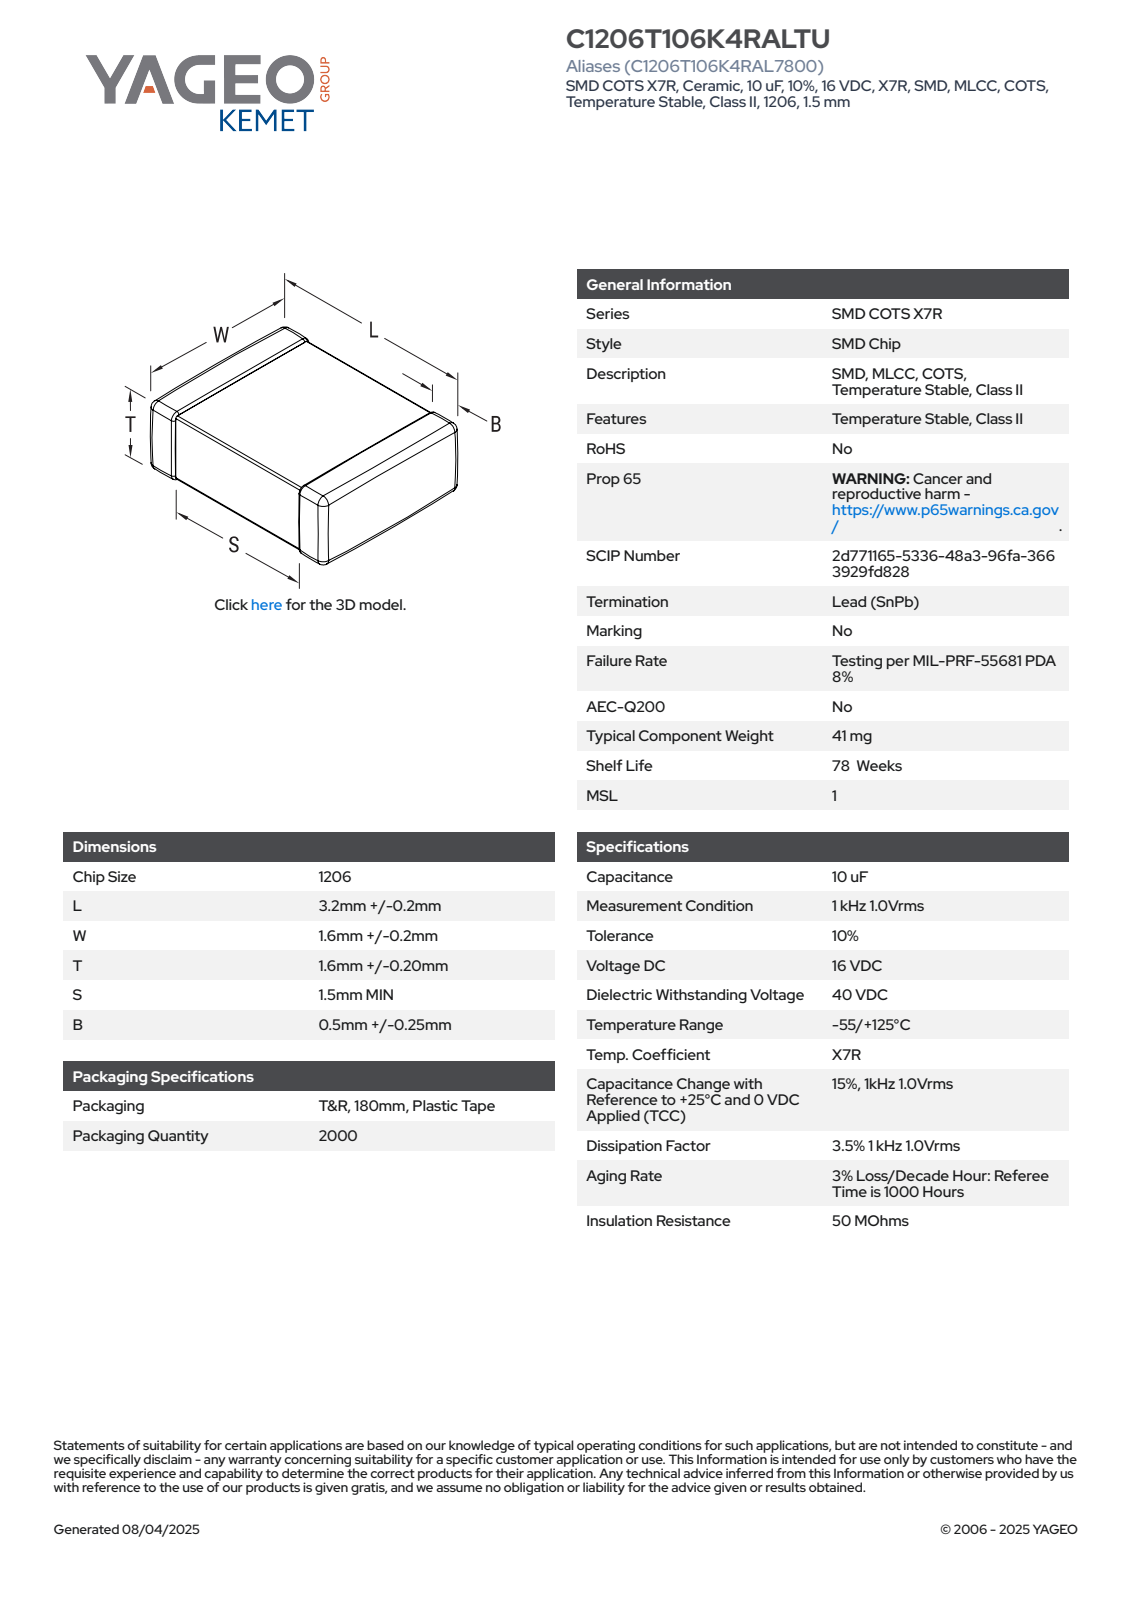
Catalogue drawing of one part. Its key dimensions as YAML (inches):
part_name: "CCS_STDNOS_1206_L3.4W1.8T1.8B0.5"
step_written_by: "SolidWorks 2014 (AUTOMOTIVE_DESIGN)"
units: inches
bodies: {solids: 4, faces: 121, planar: 71, cylindrical: 34, other: 16}
overall_size: [0.134, 0.071, 0.071]
volume: 0.001
surface_area: 0.048
face_to_face_distances: [0.068, 0.069, 0.134, 0.071, 0.07, 0.068, 0.028, 0.027, 0.041, 0.043]
